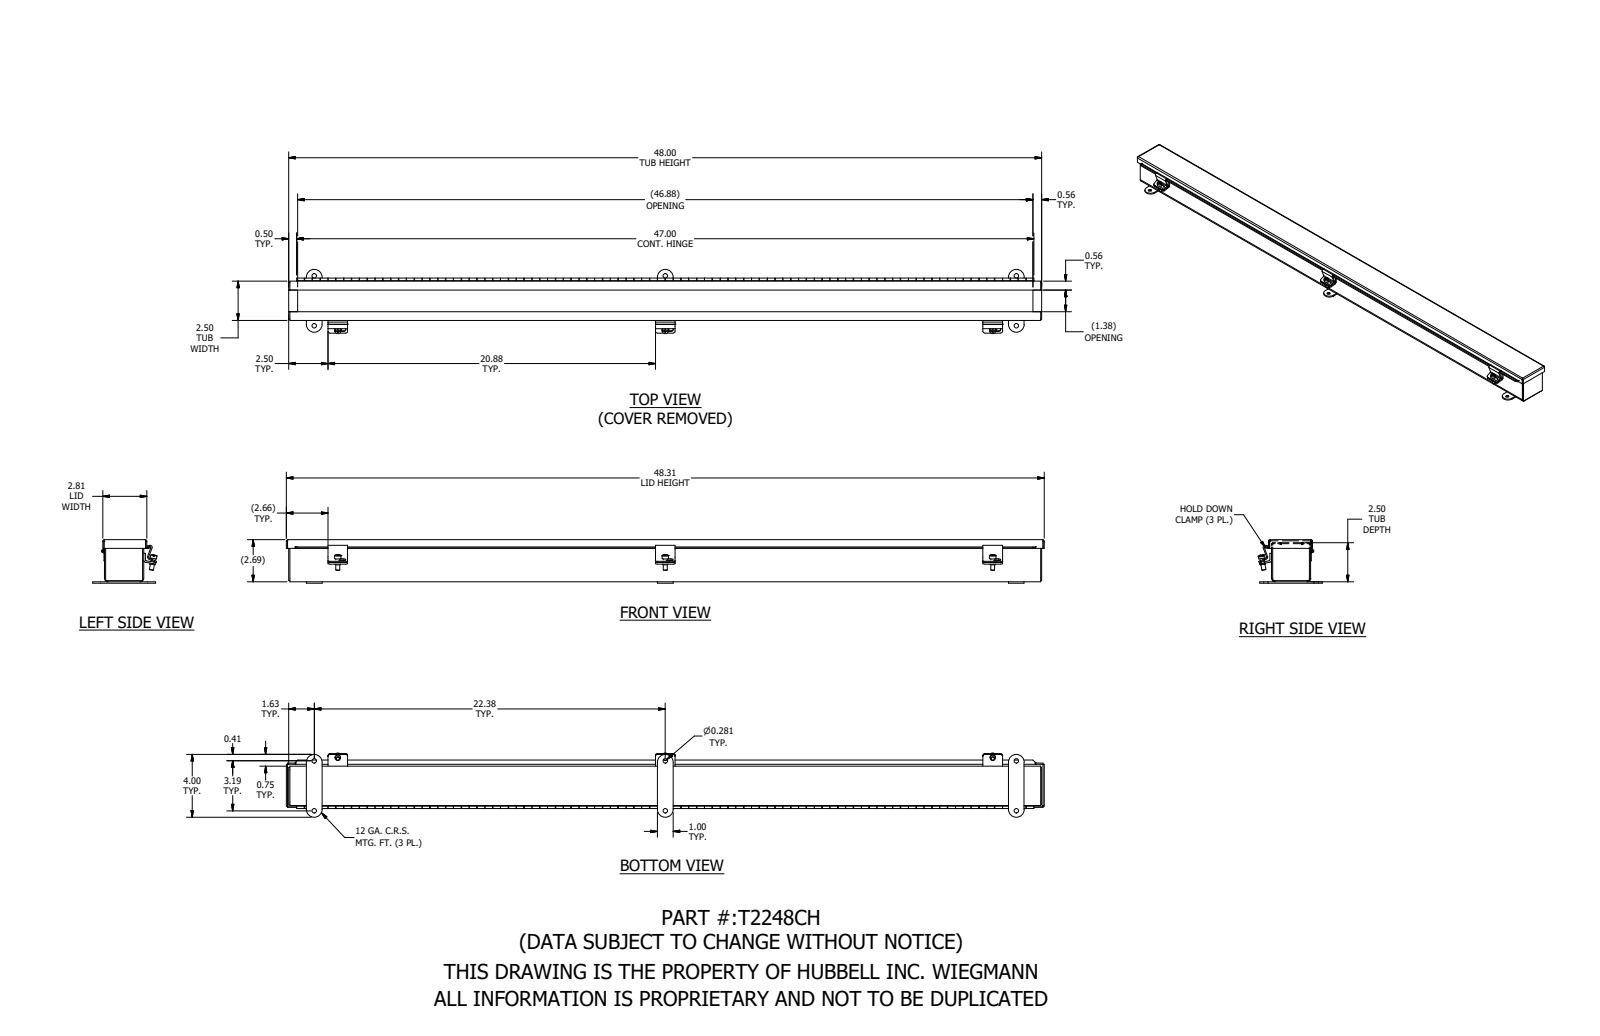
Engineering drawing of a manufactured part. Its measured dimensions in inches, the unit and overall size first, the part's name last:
Units: inches
Overall size (bounding box): 48.313 × 4.095 × 2.783
Round holes (diameter × count): ⌀0.281 ×6, ⌀0.196 ×3, ⌀0.116 ×1
Round bosses / shafts (diameter × count): ⌀0.41 ×3, ⌀0.344 ×3, ⌀0.25 ×3, ⌀0.2 ×1, ⌀0.1 ×1
Partial cylindrical surfaces — rounded edges, fillets, slot ends (radius × count): R0.125 ×12, R0.031 ×9, R0.105 ×9, R0.133 ×6, R0.5 ×6, R0.063 ×3, R0.126 ×3, R0.156 ×2
Main face-to-face distances: 0.074, 2.426, 2.615, 2.5, 2.352, 2.689, 2.541, 2.542, 0.116, 0.189
Hole centre spacings: 3.187, 22.375, 22.375, 22.601, 22.601, 44.75, 44.863, 20.875
Volume: 49.14 in³ · Surface area: 1 416 in²
Bodies: 19 solids, 993 faces (486 planar, 484 cylindrical, 23 other)
Part name (STEP PRODUCT): T2248CH
STEP written by: SolidWorks 2021 (AUTOMOTIVE_DESIGN)
